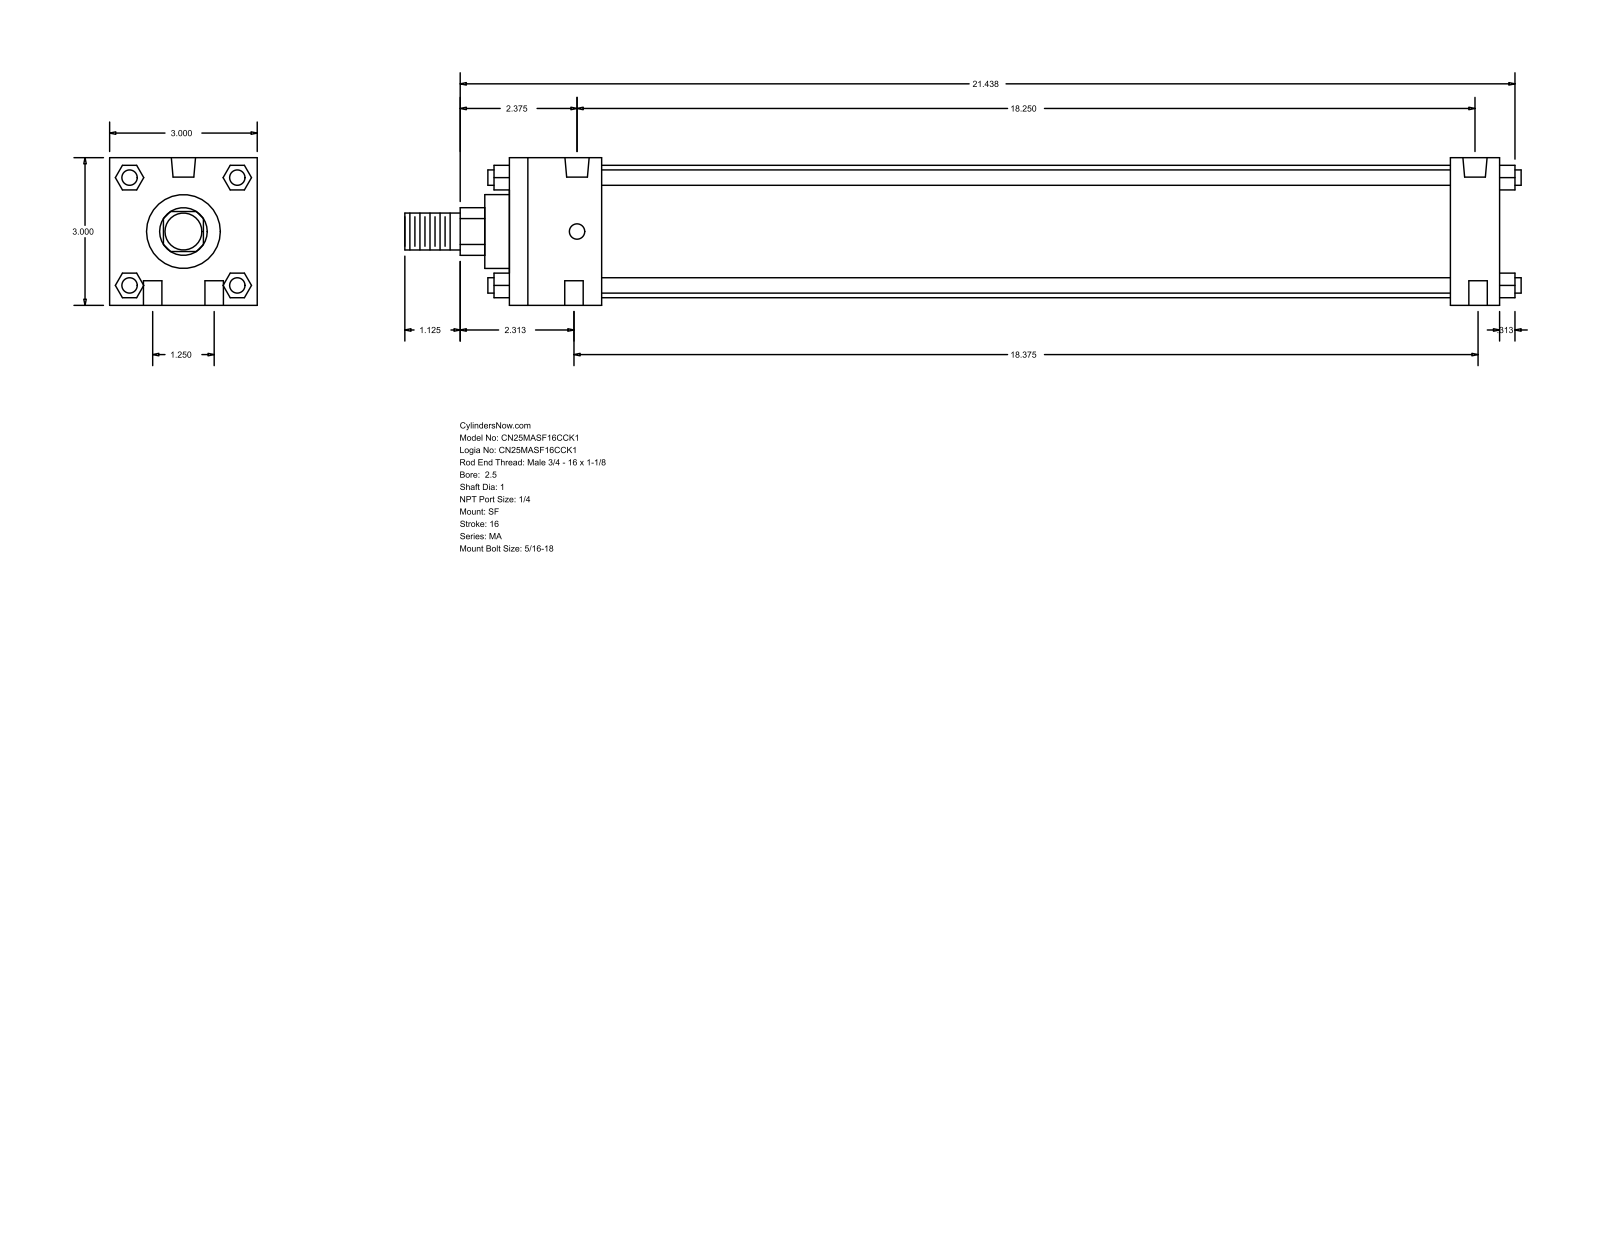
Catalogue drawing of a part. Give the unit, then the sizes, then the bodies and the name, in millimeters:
Units: millimetres
Overall size (bounding box): 576.26 × 76.2 × 76.2
Round holes (diameter × count): ⌀9.53 ×4, ⌀7.94 ×2, ⌀12.49 ×2
Round bosses / shafts (diameter × count): ⌀7.94 ×4, ⌀68.33 ×1, ⌀38.1 ×1, ⌀25.4 ×1, ⌀19.05 ×1
Partial cylindrical surfaces — rounded edges, fillets, slot ends (radius × count): R12.29 ×1
Main face-to-face distances: 76.2, 511.18, 12.7, 25.4, 485.78, 47.63, 438.15, 463.55, 27.81, 48.17
Hole centre spacings: 15.96, 31.76, 463.55, 465.4, 465.41, 466.72, 467.8
Bodies: 0 solids, 124 faces (94 planar, 30 cylindrical, 0 other)
Part name (STEP PRODUCT): MA_SF__0250_1
STEP written by: GSSL Pune (CONFIG_CONTROL_DESIGN)
